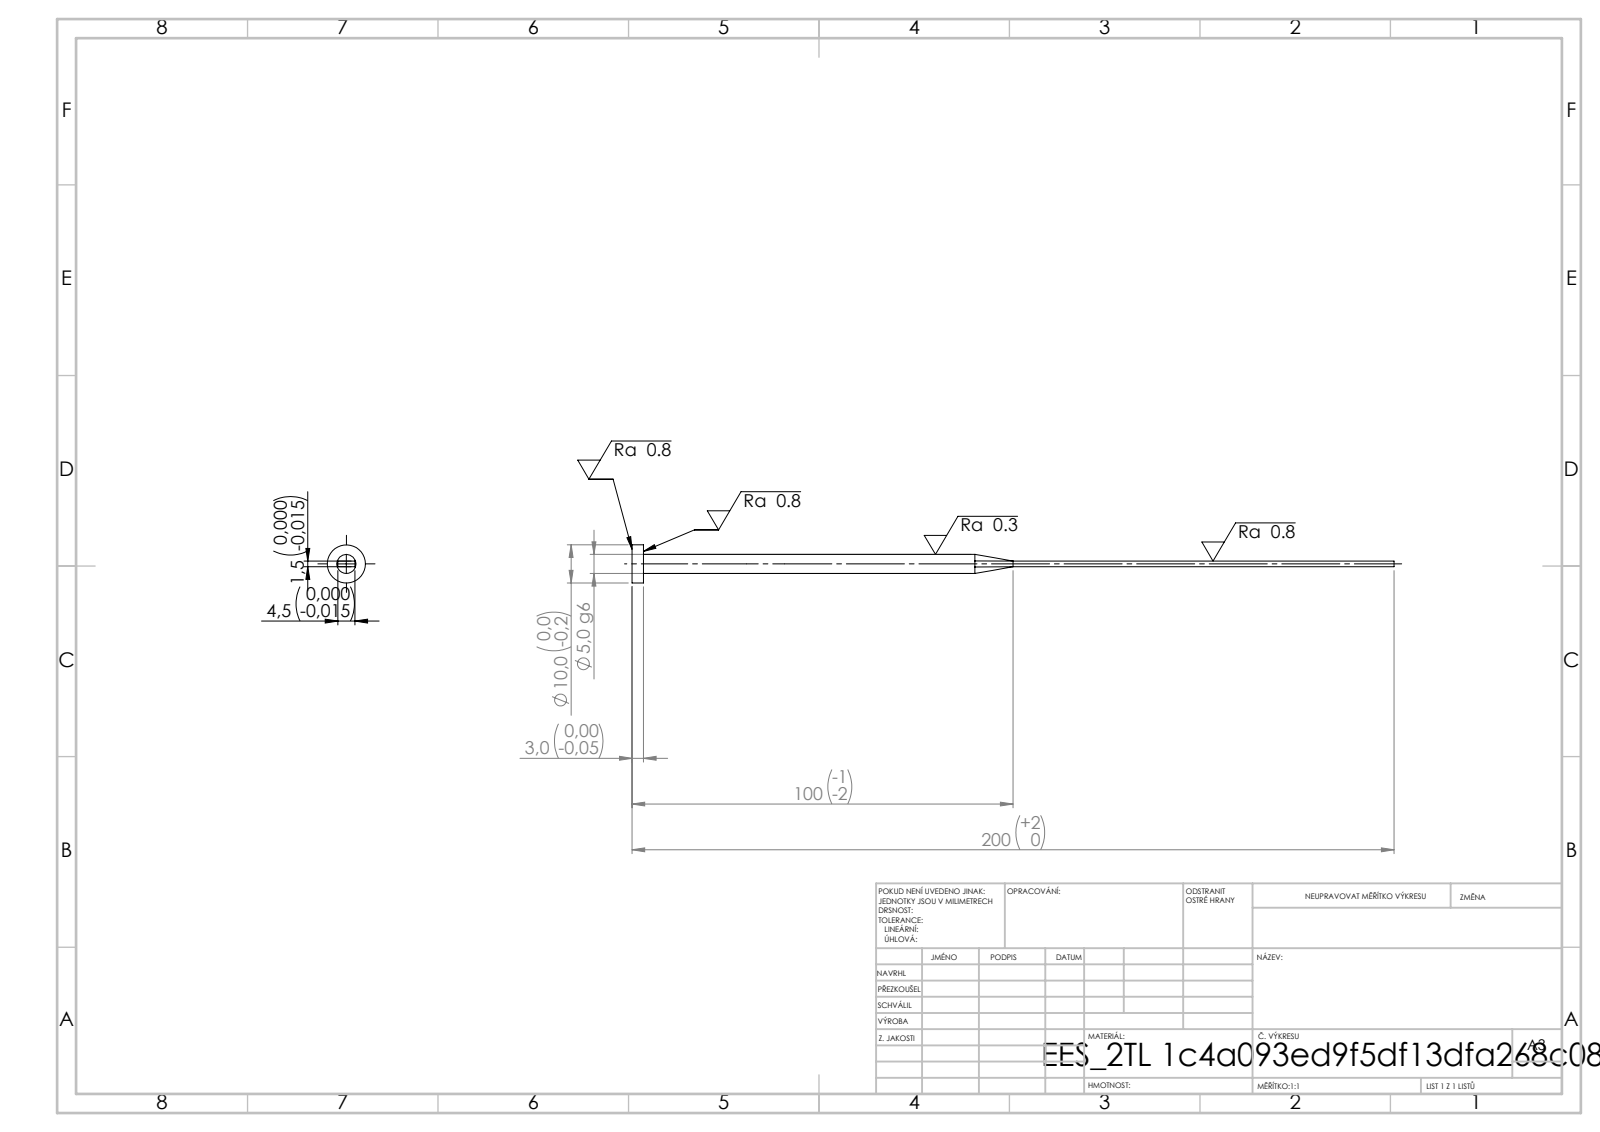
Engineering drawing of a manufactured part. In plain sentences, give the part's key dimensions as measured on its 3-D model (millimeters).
Its 3-D file was written by "SolidWorks 2019 (CONFIG_CONTROL_DESIGN)". It is 1 solid with 15 faces: 7 planar, 4 cylindrical and 4 other. Overall it measures 200 by 10 by 10 millimeters. Its volume is 2 747 cubic millimeters and its surface area 2 940 square millimeters. Round bosses or shafts: 1 of diameter 10, 1 of diameter 5. The main face-to-face distances are 1.5, 4.5, 3, 200, 197.
